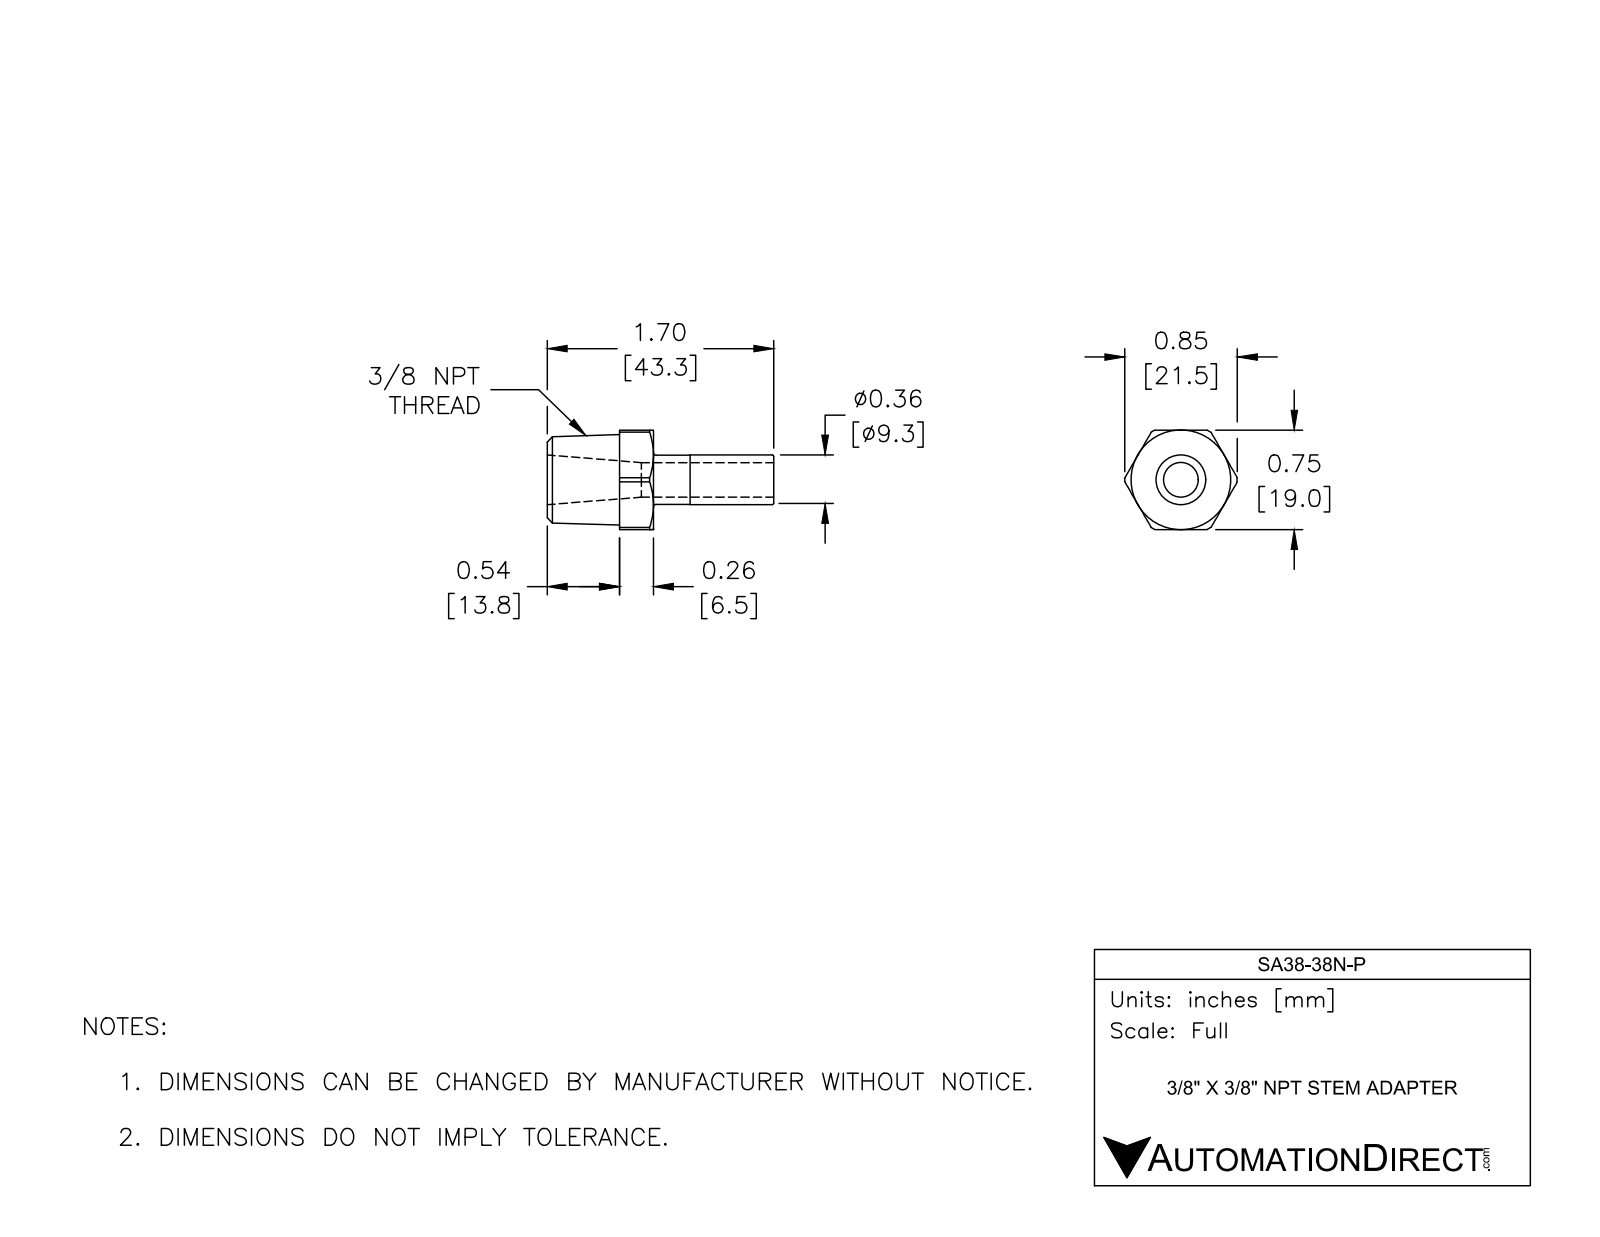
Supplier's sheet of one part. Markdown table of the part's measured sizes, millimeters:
| quantity | value |
| --- | --- |
| part name | SA38-38N-P |
| STEP written by | SolidWorks 2017 (AUTOMOTIVE_DESIGN) |
| units | millimeters |
| bodies | 1 solid, 41 faces (11 planar, 13 cylindrical, 17 other) |
| overall size | 43.3 × 21.5 × 19 |
| volume | 4 920 mm³ |
| surface area | 3 265 mm² |
| round holes (diameter × count) | 6.6 × 1 |
| round bosses / shafts (diameter × count) | 9.5 × 1, 9.4 × 1 |
| partial cylindrical surfaces (radius × count) | 10.7 × 1 |
| main face-to-face distances | 19, 20.3, 13.8, 6.5, 43.3, 29.5, 23, 27.3, 13.5, 7 |
